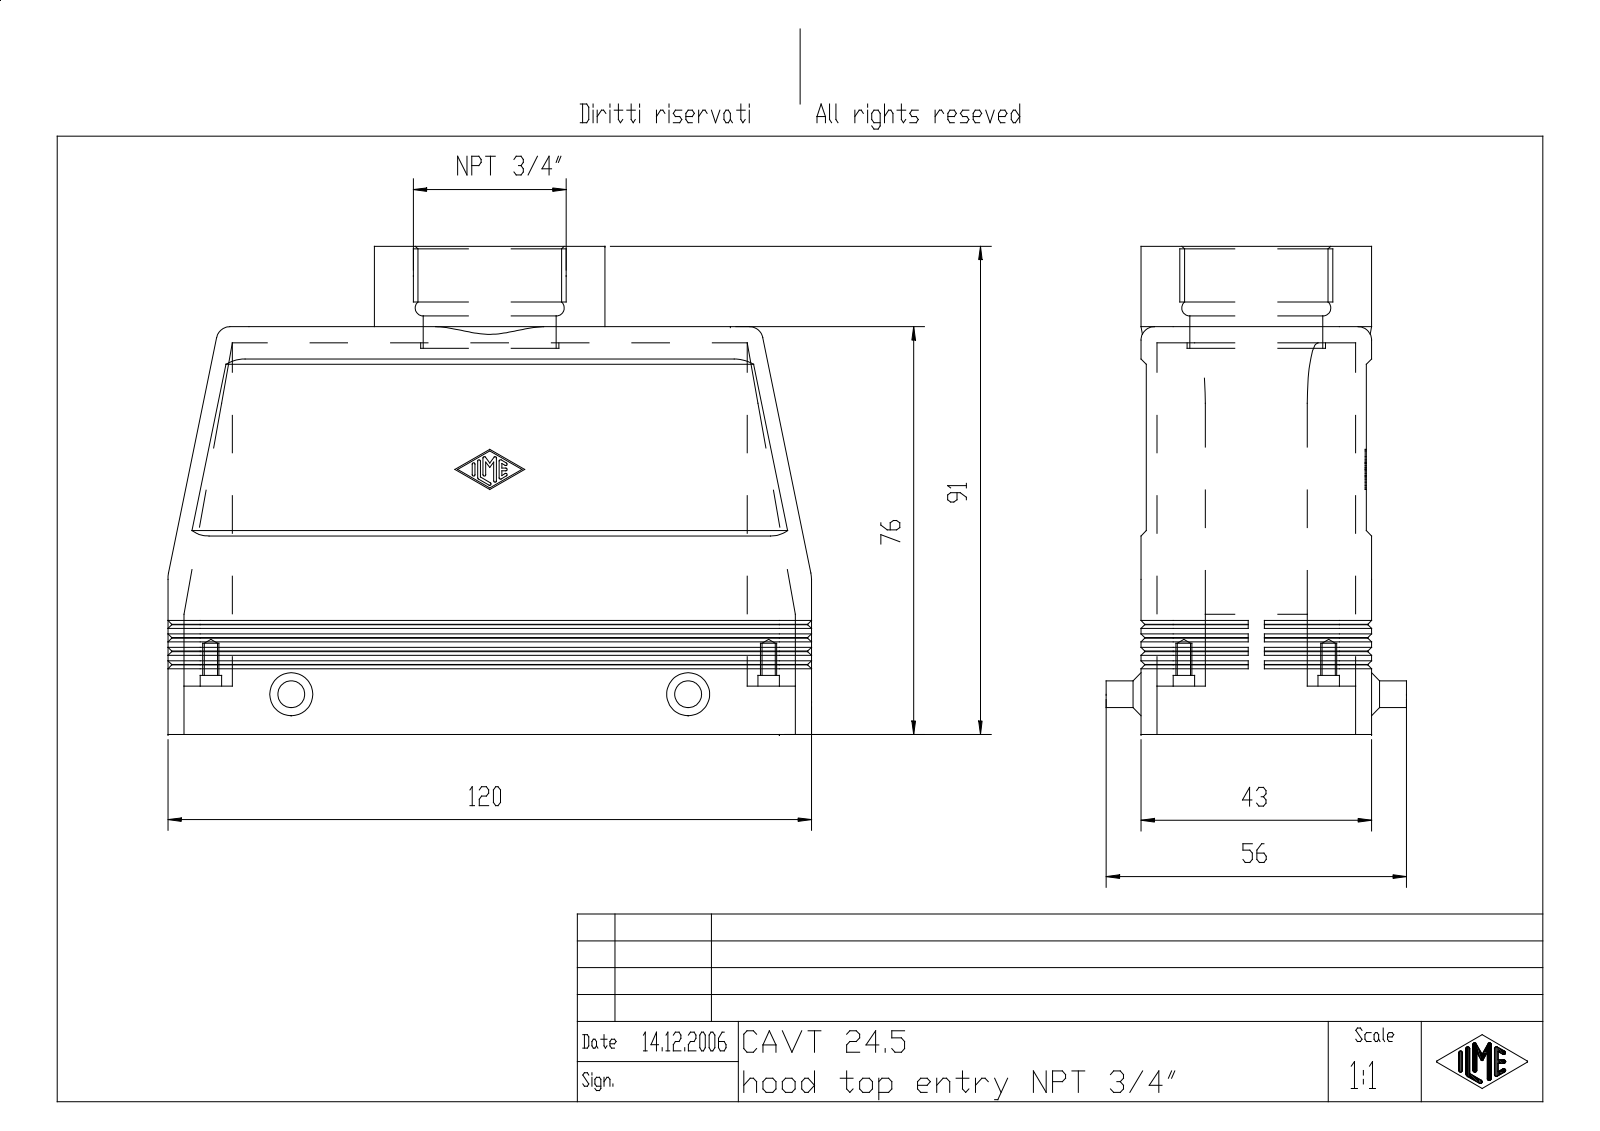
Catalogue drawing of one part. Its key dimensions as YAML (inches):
part_name: "MSBO6813"
step_written_by: "Creo Elements/Direct Modeling 18.0B 02-Dec-2011 (C) Parametric Technology GmbH (AUTOMOTIVE_DESIGN)"
units: inches
bodies: {solids: 1, faces: 338, planar: 180, cylindrical: 99, other: 59}
overall_size: [4.724, 3.583, 2.205]
volume: 6.098
surface_area: 88.48
round_holes:
  - {diameter: 0.157, count: 4}
  - {diameter: 0.097, count: 3}
  - {diameter: 0.097, count: 1}
round_bosses_or_shafts:
  - {diameter: 0.197, count: 2}
  - {diameter: 1.693, count: 1}
partial_cylinders:
  - {radius: 0.01, count: 14}
  - {radius: 0.236, count: 10}
  - {radius: 0.079, count: 4}
  - {radius: 0.098, count: 4}
  - {radius: 0.118, count: 4}
  - {radius: 0.209, count: 4}
face_to_face_distances: [0.118, 0.039, 1.575, 1.457, 0.079, 1.654, 1.535, 1.693, 1.614, 0.472]
hole_center_spacings: [1.063, 4.094, 4.23]
